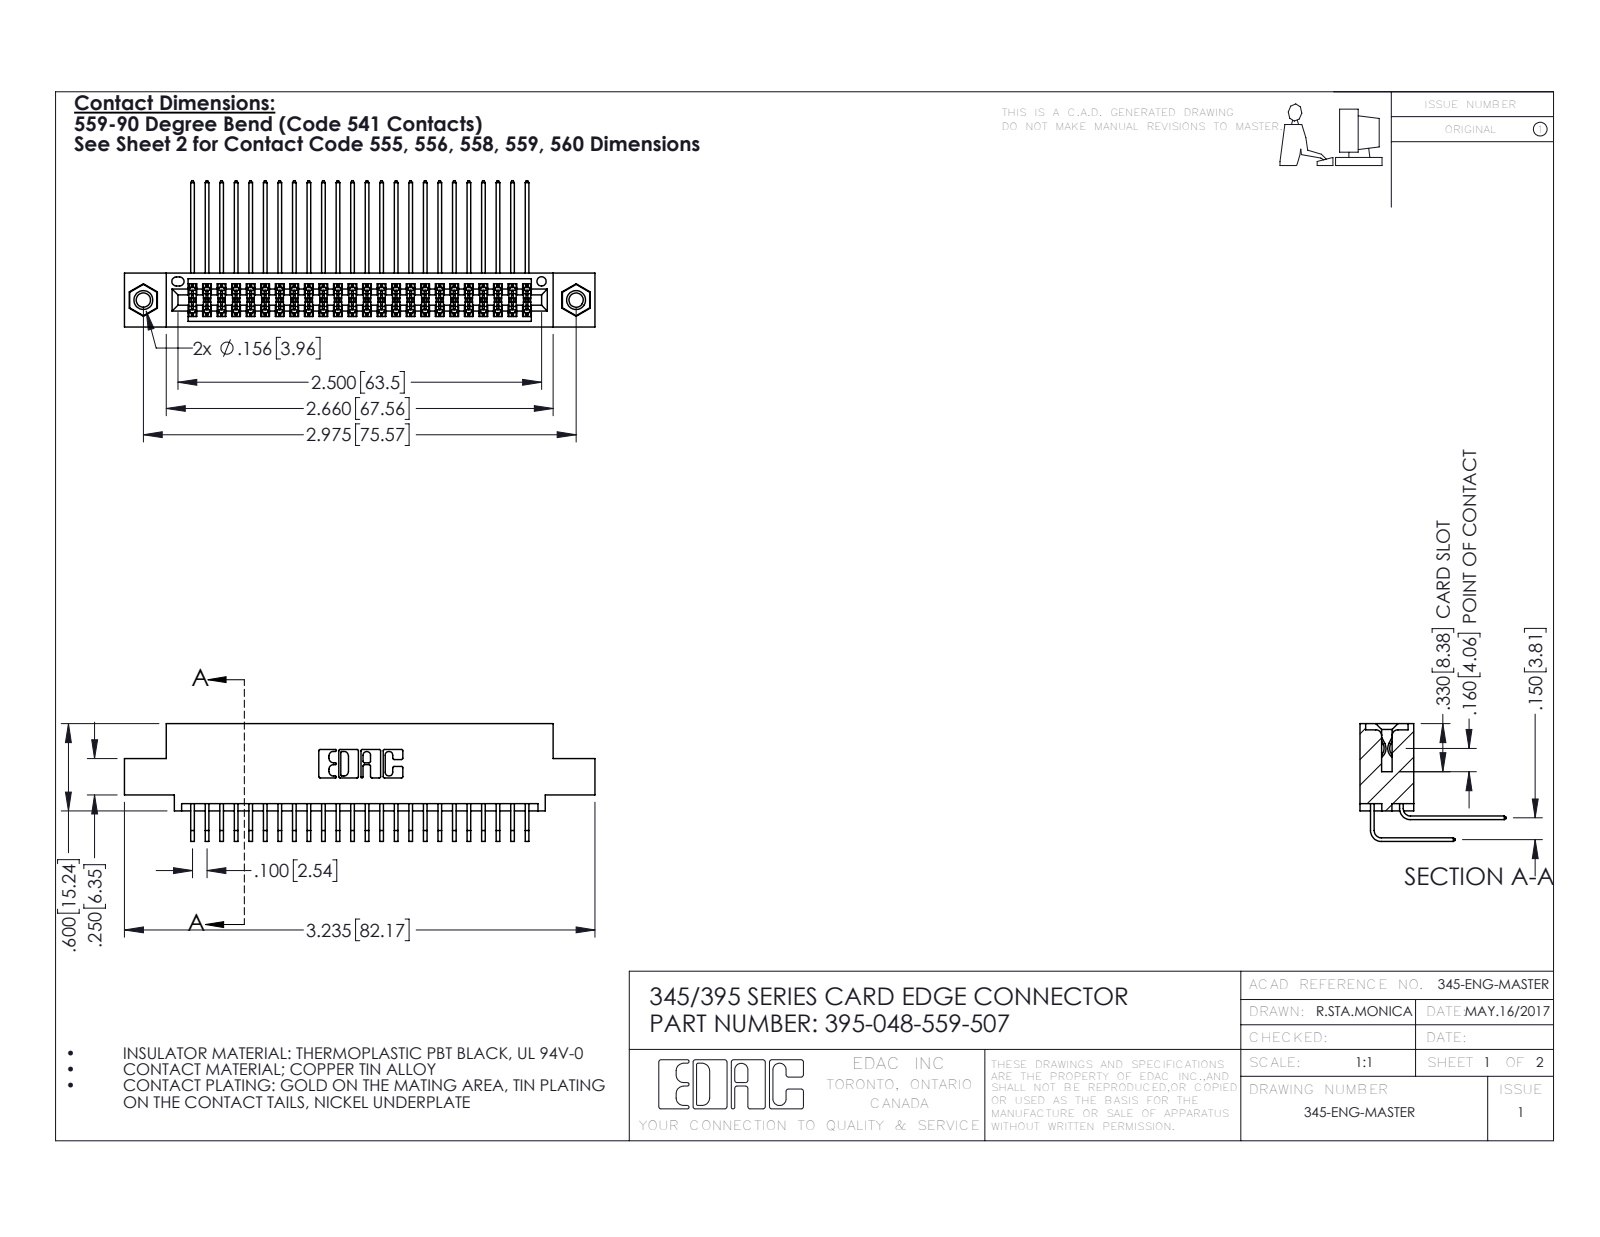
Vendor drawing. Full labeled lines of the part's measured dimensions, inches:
Part name (STEP PRODUCT): 345-250-001_345-250-005-103; 345-292-001_558 559 Tail - 1; 395-048-559-507; 345 Part_0.110 Offset - 0.156 Dia-TI (+1 more)
STEP written by: SolidWorks 2016 (CONFIG_CONTROL_DESIGN)
Units: inches
Bodies: 51 solids, 2686 faces (1796 planar, 874 cylindrical, 16 other)
Overall size (bounding box): 3.235 × 1.005 × 0.809
Volume: 0.488 in³ · Surface area: 20.01 in²
Round holes (diameter × count): ⌀0.098 ×2, ⌀0.125 ×2, ⌀0.156 ×2, ⌀0.064 ×1
Round bosses / shafts (diameter × count): ⌀0.155 ×2
Partial cylindrical surfaces — rounded edges, fillets, slot ends (radius × count): R0.006 ×72, R0.01 ×22, R0.007 ×6, R0.031 ×6, R0.026 ×3, R0.014 ×2, R0.019 ×2, R0.022 ×2
Main face-to-face distances: 0.072, 0.298, 0.2, 0.37, 0.098, 0.272, 0.025, 0.225, 0.15, 0.175
Hole centre spacings: 0.27, 2.741, 2.975
